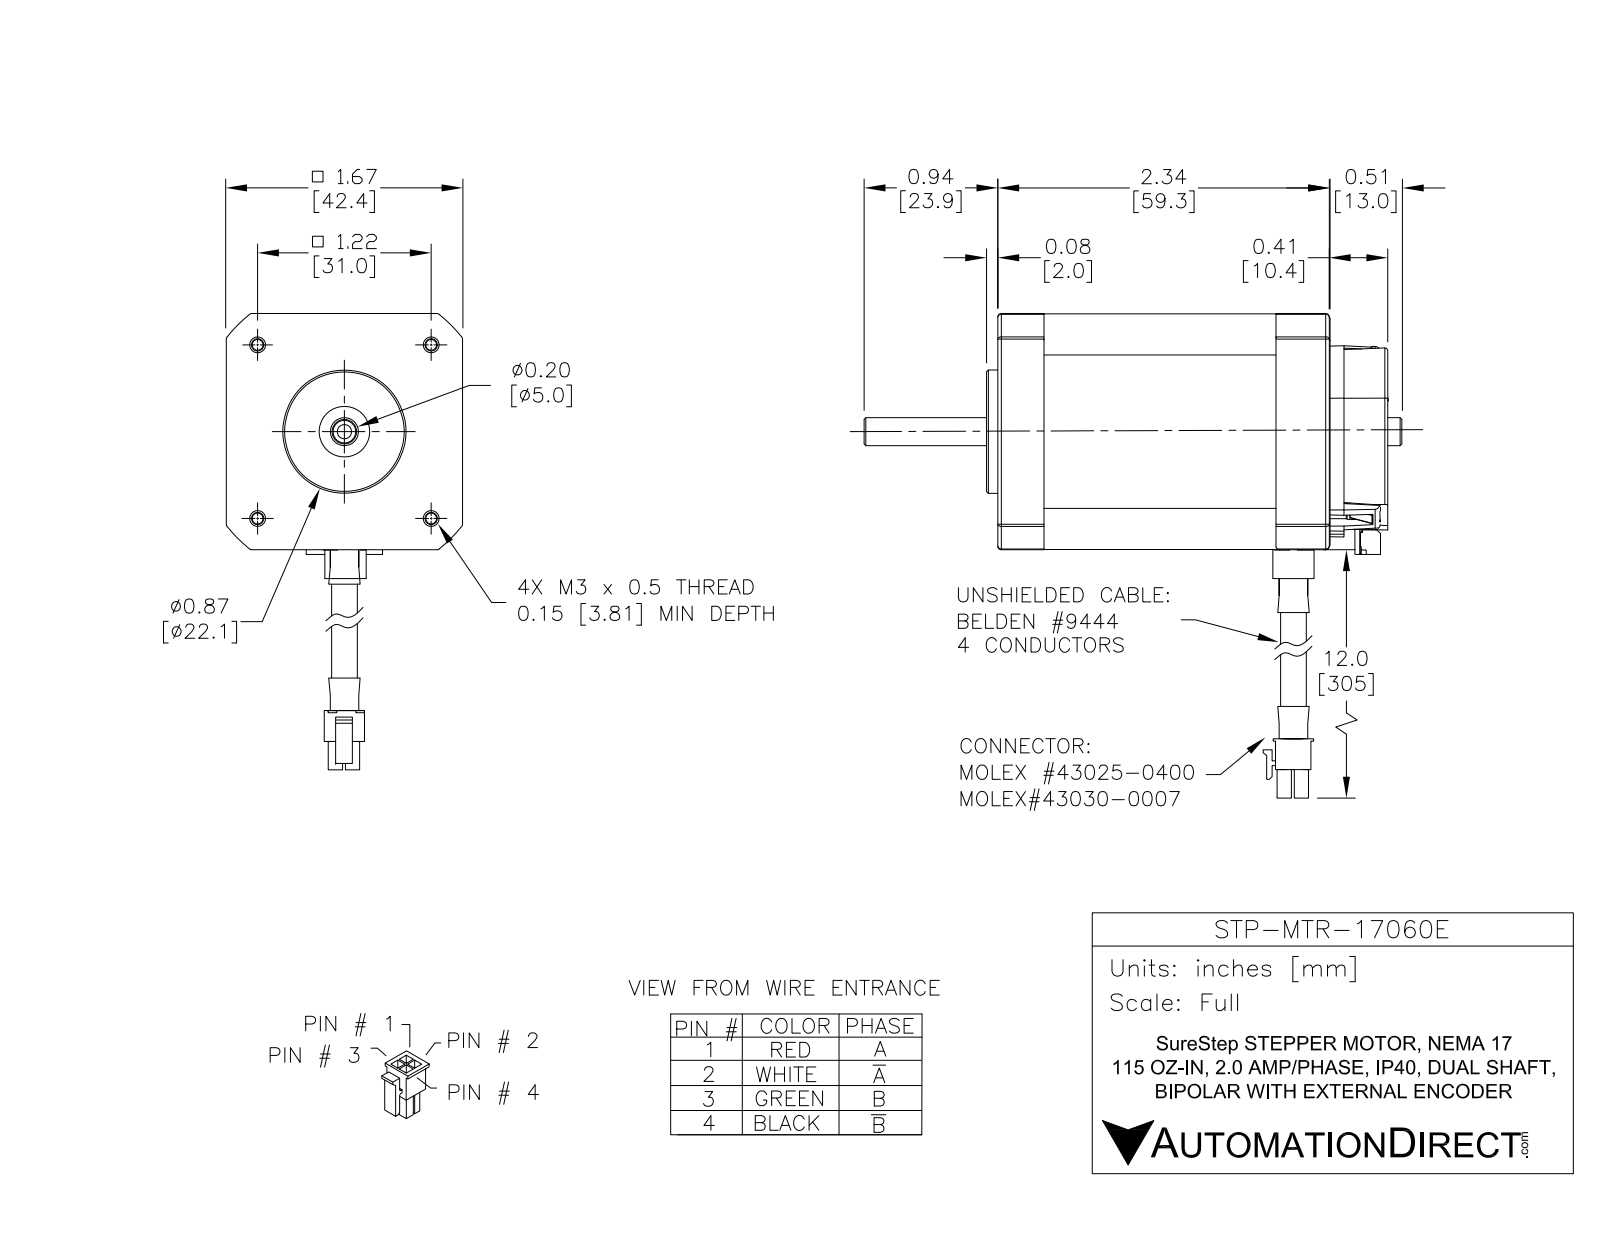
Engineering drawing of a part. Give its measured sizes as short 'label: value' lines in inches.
name: STP-MTR-17060E
written by: SolidWorks 2017 (AUTOMOTIVE_DESIGN)
unit: in
bodies: 15 solids, 1645 faces (968 planar, 390 cylindrical, 287 other)
size: 13.976 × 3.78 × 1.66
volume: 6.974 in³; area: 48.45 in²
holes: 7× ⌀0.079, 4× ⌀0.031, 4× ⌀0.037, 4× ⌀0.086, 4× ⌀0.15, 2× ⌀0.067, 2× ⌀0.091, 2× ⌀0.116, 2× ⌀0.161, 2× ⌀0.177, 1× ⌀0.05, 1× ⌀0.25
bosses: 4× ⌀0.13, 4× ⌀0.059, 1× ⌀0.866, 1× ⌀0.465, 1× ⌀0.413, 1× ⌀0.29, 1× ⌀0.217, 1× ⌀0.197
rounds: 22× R0.039, 17× R0.025, 6× R0.02, 6× R0.041, 6× R0.079, 4× R0.012, 4× R0.016, 4× R0.08
face distances: 1.656, 1.658, 2.335, 1.66, 0.209, 2.544, 0.175, 0.098, 0.033, 2.51
hole spacings: 0.997, 0.212, 0.354, 0.5, 0.707, 0.997, 1.159, 1.22
